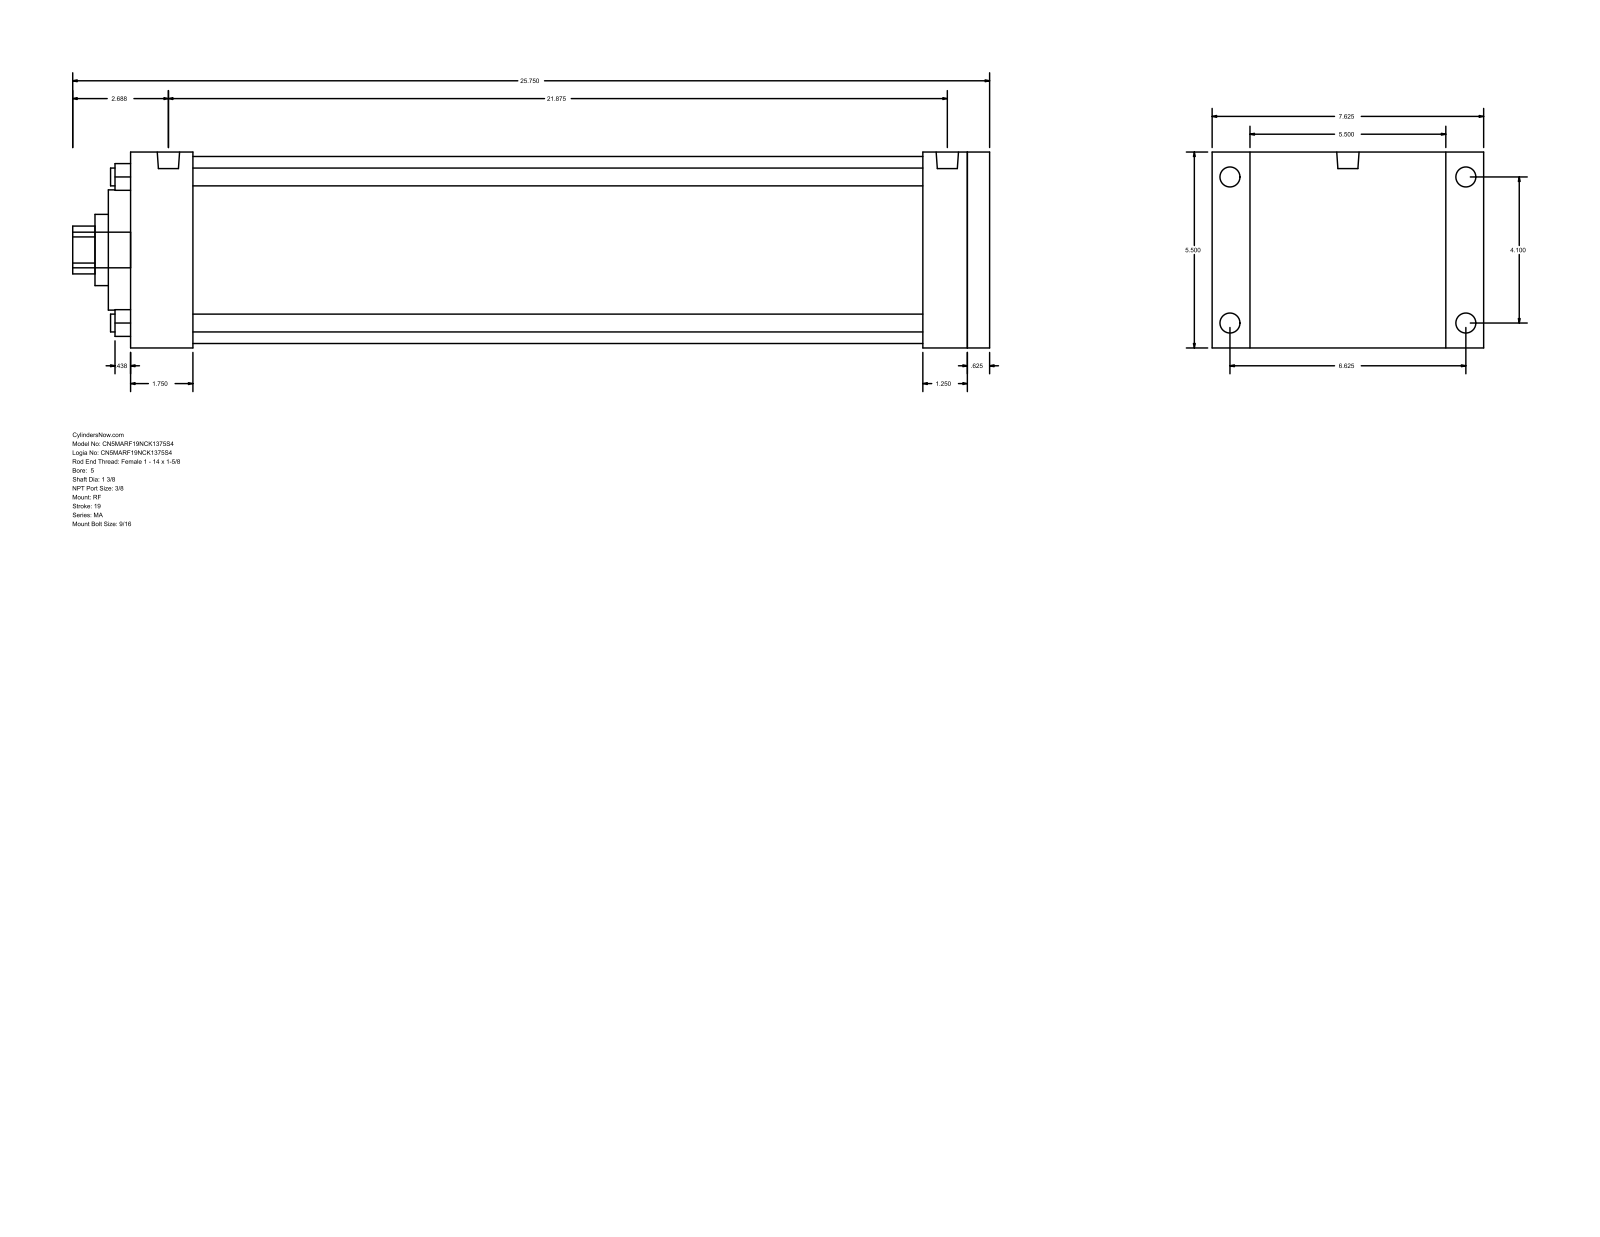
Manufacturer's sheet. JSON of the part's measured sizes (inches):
{"part_name": "MA_RF__0500_1.375", "step_written_by": "GSSL Pune (CONFIG_CONTROL_DESIGN)", "units": "inches", "bodies": {"solids": 0, "faces": 94, "planar": 65, "cylindrical": 29, "other": 0}, "overall_size": [25.75, 7.625, 5.5], "round_holes": [[0.5, 4], [1.375, 1], [2, 1], [3.375, 1], [5.25, 1]], "round_bosses_or_shafts": [[0.563, 4], [0.437, 4], [0.627, 2], [1, 1]], "partial_cylinders_radius": [[0.672, 1]], "face_to_face_distances": [5.5, 24.125, 0.625, 23.5, 1.75, 21.75, 22.375, 22.25, 20.5, 1.25], "hole_center_spacings": [2.899, 4.1, 5.798]}
